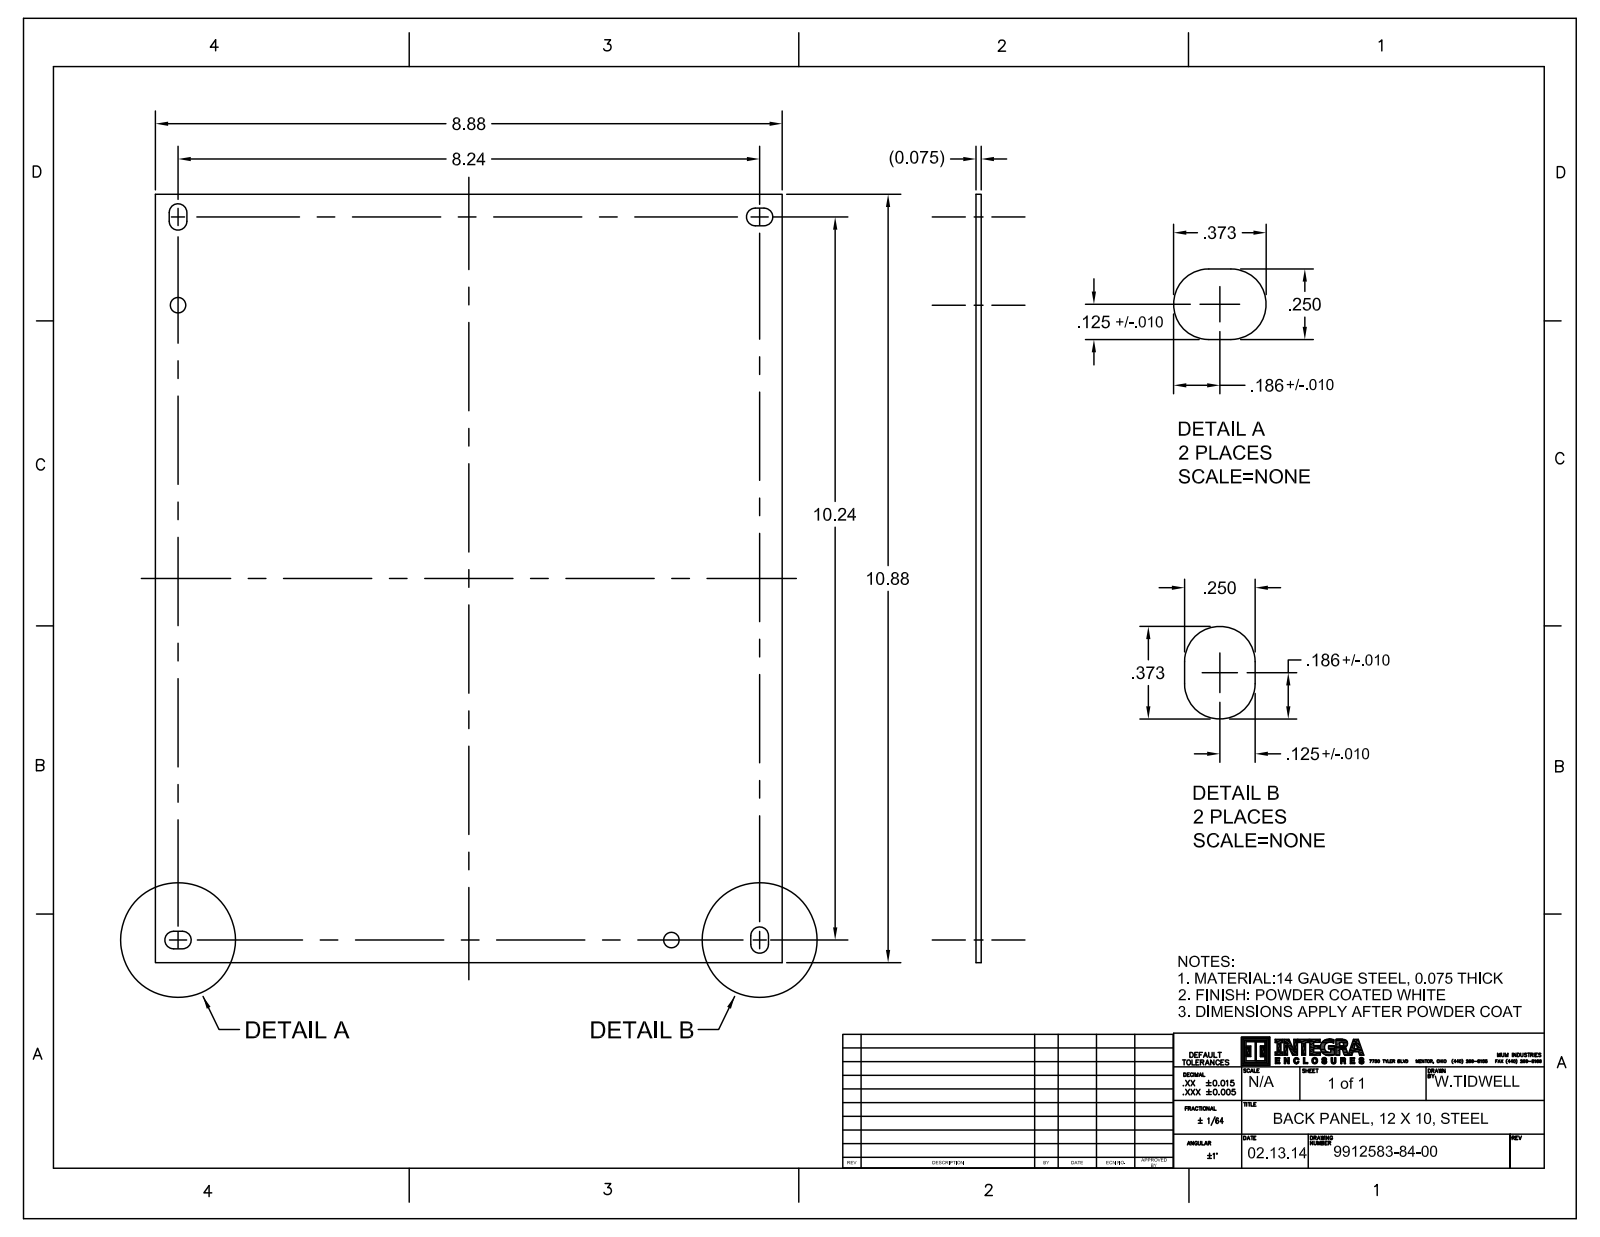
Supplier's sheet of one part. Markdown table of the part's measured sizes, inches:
| quantity | value |
| --- | --- |
| part name | 9912583-84-00; 9912518-82-10; SBP1210_ASM |
| STEP written by | CREO PARAMETRIC BY PTC INC, 2016050 (CONFIG_CONTROL_DESIGN) |
| units | inches |
| bodies | 5 solids, 434 faces (90 planar, 272 cylindrical, 72 other) |
| overall size | 10.88 × 8.88 × 0.443 |
| volume | 7.255 in³ |
| surface area | 198.3 in² |
| round holes (diameter × count) | 0.219 × 2 |
| round bosses / shafts (diameter × count) | 0.373 × 4, 0.19 × 4, 0.149 × 4 |
| partial cylindrical surfaces (radius × count) | 0.004 × 48, 0.125 × 8 |
| main face-to-face distances | 0.075, 8.88, 10.88, 0.238, 0.313, 0.195, 0.445, 0.25, 8.207, 10.199 |
| hole center spacings | 11.388 |
